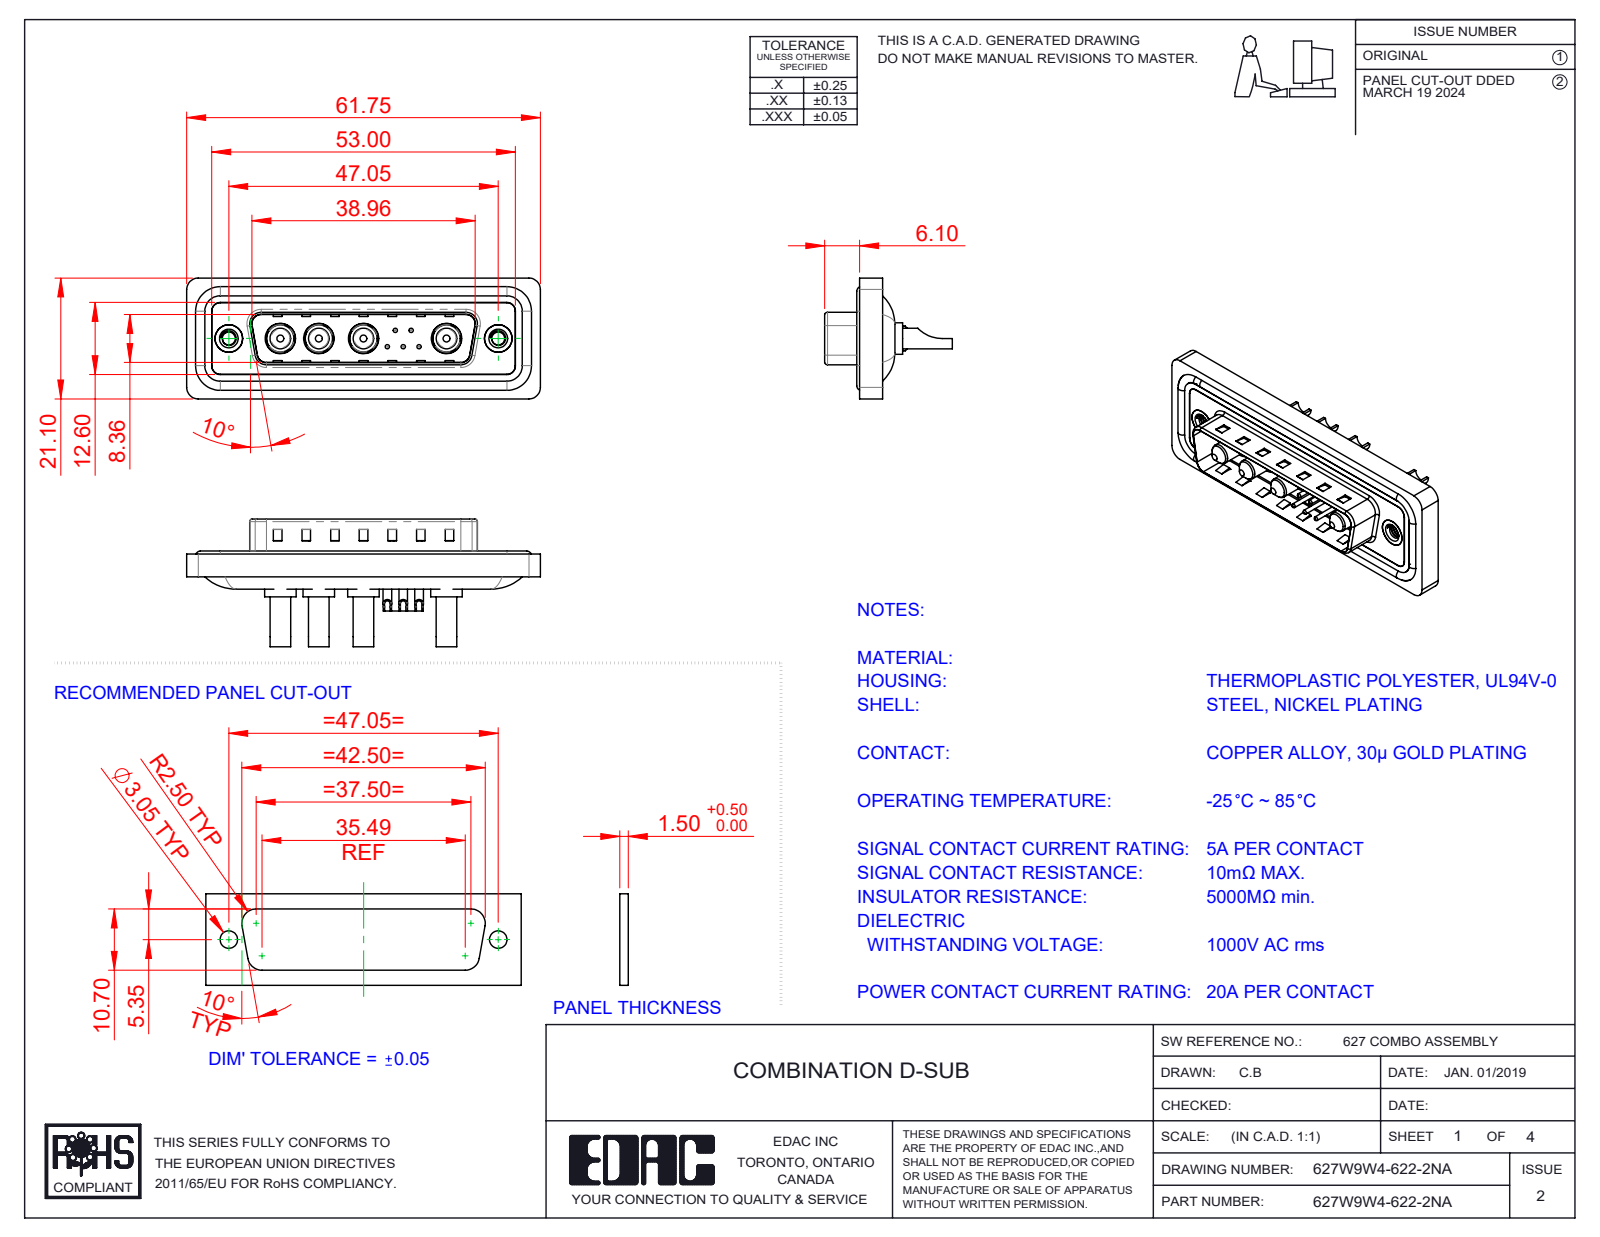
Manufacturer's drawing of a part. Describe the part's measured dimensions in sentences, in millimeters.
The part is named "627Combo Contact Row 1_22; 627Combo Threaded Rivet_A; 627Combo Waterproof Housing_25 Contacts; 627Combo Shell Front_25 Contacts (+5 more)". Its 3-D file was written by "SolidWorks 2023 (CONFIG_CONTROL_DESIGN)". It is 20 solids with 850 faces: 306 planar, 358 cylindrical and 186 other. Overall it measures 61.75 by 22.3 by 21.1 millimeters. Its volume is 7 465 cubic millimeters and its surface area 12 203 square millimeters. Round holes: 5 of diameter 0.75, 5 of diameter 1, 5 of diameter 1.6, 5 of diameter 2, 4 of diameter 2.7, 4 of diameter 4.85, 4 of diameter 5.3, 2 of diameter 2.26, 2 of diameter 4, 2 of diameter 4.8, 2 of diameter 5. Round bosses or shafts: 5 of diameter 1.5, 4 of diameter 5.5, 4 of diameter 5.2, 4 of diameter 4.75, 4 of diameter 3.75, 4 of diameter 3.6, 4 of diameter 1.6, 2 of diameter 4.9. Partial cylindrical surfaces (rounded edges, fillets, slot ends): 22 of radius 1.5, 18 of radius 2, 8 of radius 0.5, 8 of radius 1.6, 6 of radius 1, 4 of radius 0.25, 4 of radius 0.6, 4 of radius 0.65. The main face-to-face distances are 0.4, 1.5, 1.1, 0.5, 1.6, 3.1, 2.9, 0.82, 9.58, 5.65. The hole center spacings are 3.16, 2.77, 5.04, 14.51, 2.78, 4.4, 4.41, 5.
